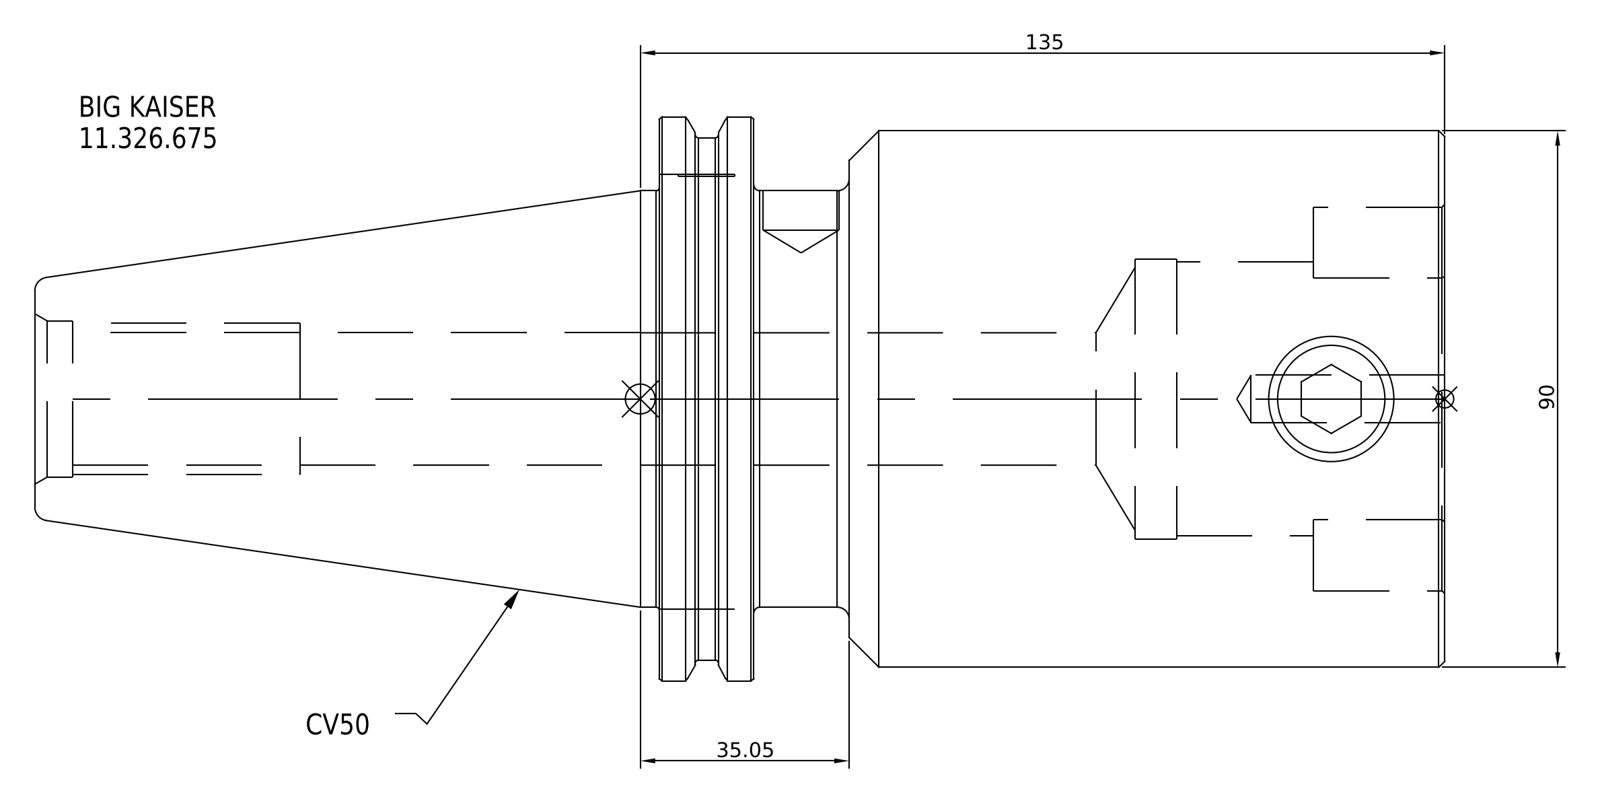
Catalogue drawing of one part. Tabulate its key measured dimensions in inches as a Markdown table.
| quantity | value |
| --- | --- |
| part name | 11.326.675 |
| STEP written by | SolidWorks 2021 (CONFIG_CONTROL_DESIGN) |
| units | inches |
| bodies | 1 solid, 16 faces (7 planar, 6 cylindrical, 3 other) |
| overall size | 9.315 × 3.875 × 3.875 |
| volume | 65.84 in³ |
| surface area | 115.2 in² |
| round bosses / shafts (diameter × count) | 3.875 × 1, 3.594 × 1, 3.543 × 1, 2.75 × 1 |
| main face-to-face distances | 5.256, 4.565, 0.691, 3.937, 0.628, 1.319, 9.315, 5.378, 4.75, 4.059 |
